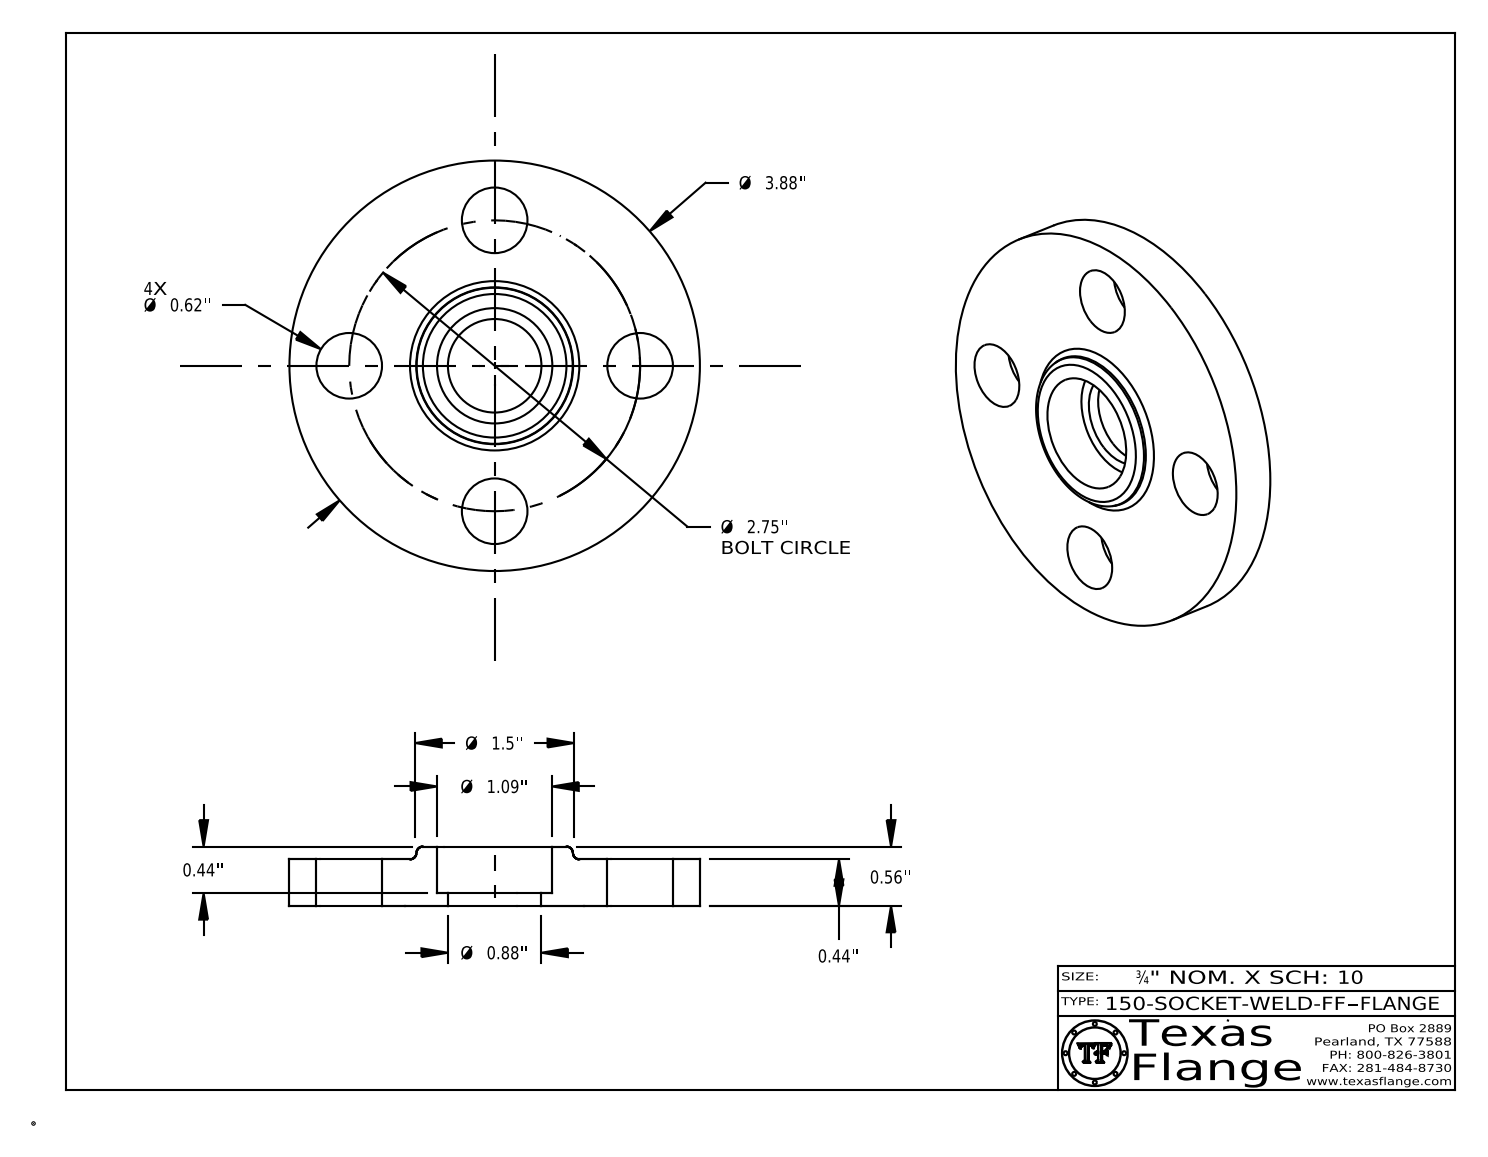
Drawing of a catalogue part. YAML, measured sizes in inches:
part_name: "150-SOCKET-WELD-FF"
step_written_by: "CATIA V5 STEP AP214 (AUTOMOTIVE_DESIGN)"
units: inches
bodies: {solids: 1, faces: 410, planar: 370, cylindrical: 34, other: 6}
overall_size: [3.88, 3.88, 0.56]
volume: 4.392
surface_area: 31.04
round_holes:
  - {diameter: 0.62, count: 4}
  - {diameter: 0.495, count: 1}
  - {diameter: 0.884, count: 1}
  - {diameter: 1.09, count: 1}
round_bosses_or_shafts:
  - {diameter: 0.03, count: 8}
  - {diameter: 3.88, count: 1}
  - {diameter: 0.39, count: 1}
face_to_face_distances: [0.44, 0.56, 0.12, 0.12, 0.32, 0.44, 0.425, 0.305, 0.015, 0.135]
hole_center_spacings: [1.375, 1.945, 1.052, 2.541, 2.75]
